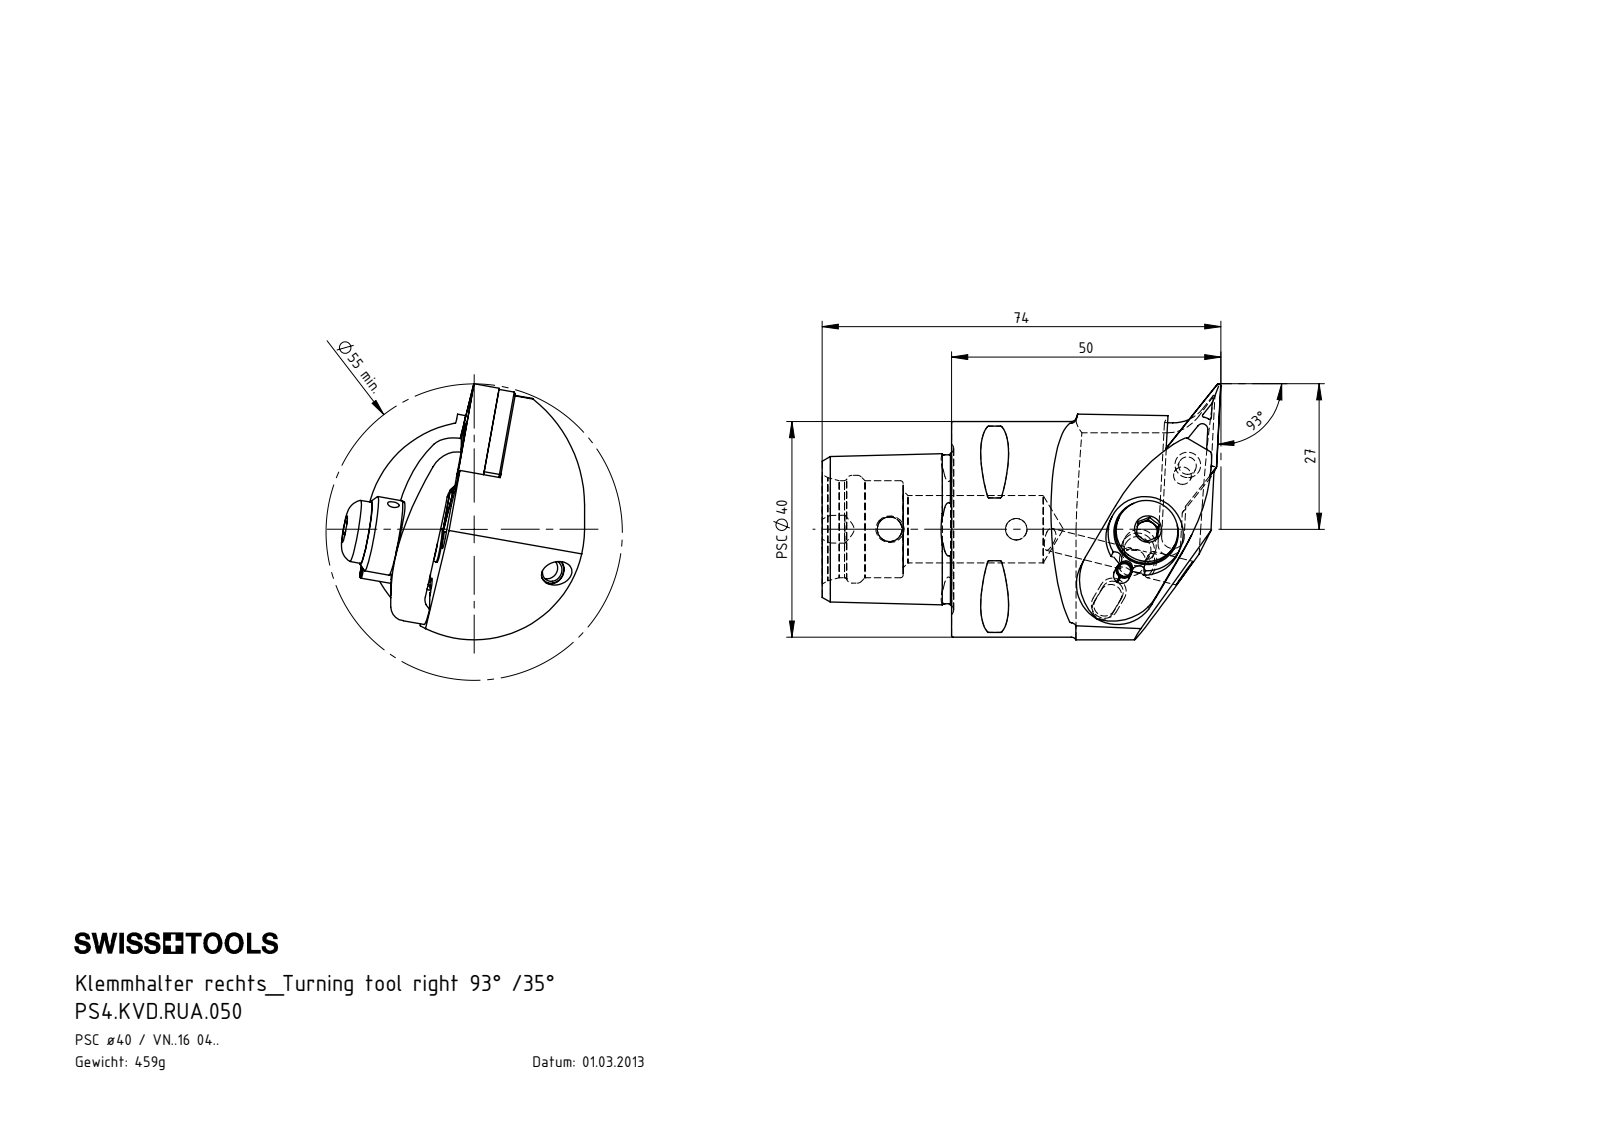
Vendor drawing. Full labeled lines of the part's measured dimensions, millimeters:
Part name (STEP PRODUCT): KVT_MB_600_050; VNMG160404; WCC-ER2.001.010_A; PS4.KVD.RUA.050 (+6 more)
STEP written by: SolidWorks 2017 (AUTOMOTIVE_DESIGN)
Units: millimetres
Bodies: 10 solids, 312 faces (99 planar, 87 cylindrical, 126 other)
Overall size (bounding box): 74 × 47.5 × 45.12
Volume: 58 445 mm³ · Surface area: 18 364 mm²
Round holes (diameter × count): ⌀2 ×3, ⌀4 ×2, ⌀5 ×2, ⌀7 ×2, ⌀2.4 ×1, ⌀3 ×1, ⌀3.3 ×1, ⌀3.8 ×1, ⌀4.2 ×1, ⌀4.6 ×1, ⌀4.95 ×1, ⌀6.2 ×1
Round bosses / shafts (diameter × count): ⌀5 ×2, ⌀40 ×1, ⌀14 ×1, ⌀11.5 ×1, ⌀7 ×1, ⌀6.8 ×1, ⌀6.2 ×1, ⌀6 ×1
Partial cylindrical surfaces — rounded edges, fillets, slot ends (radius × count): R0.3 ×8, R0.39 ×6, R0.4 ×4, R0.5 ×3, R0.69 ×3, R0.69 ×3, R1.5 ×3, R3 ×3
Main face-to-face distances: 7.64, 1.3, 3.18, 4.46, 8.94, 5.76, 9.14, 24, 9.52, 15
Hole centre spacings: 19.29, 8.02, 19.12, 8.2, 19.3, 23.5, 27.31, 27.32
